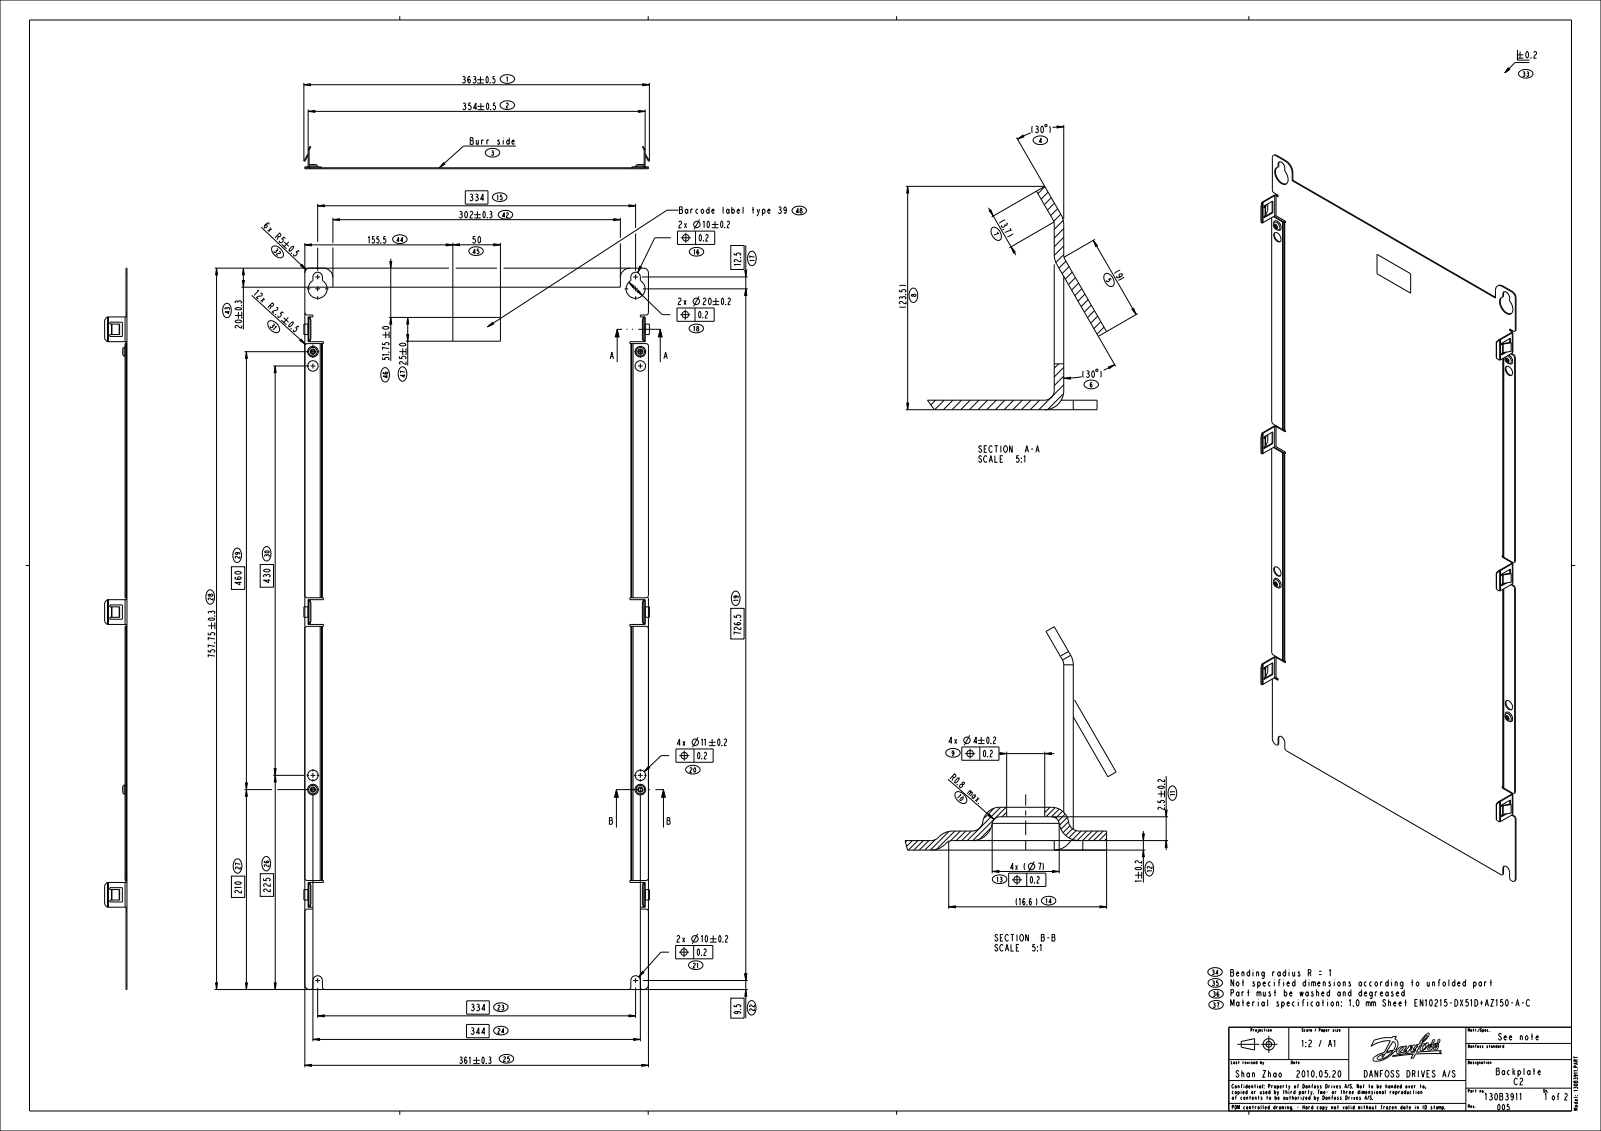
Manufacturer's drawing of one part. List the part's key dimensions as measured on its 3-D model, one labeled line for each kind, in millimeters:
Part name (STEP PRODUCT): 130B3911
STEP written by: CREO PARAMETRIC BY PTC INC, 2018070 (CONFIG_CONTROL_DESIGN)
Units: millimetres
Bodies: 1 solid, 452 faces (324 planar, 96 cylindrical, 32 other)
Overall size (bounding box): 757.75 × 363 × 23.46
Volume: 268 412 mm³ · Surface area: 540 514 mm²
Round holes (diameter × count): ⌀4 ×4, ⌀11 ×4, ⌀20 ×2
Partial cylindrical surfaces — rounded edges, fillets, slot ends (radius × count): R2.5 ×16, R1 ×10, R2 ×10, R5 ×8, R10 ×2
Main face-to-face distances: 1, 2, 353, 3.5, 4.5, 356.5, 357.5, 354, 352, 361
Hole centre spacings: 15, 344, 344.33, 445, 562.46, 66.19, 81.15, 345.37
